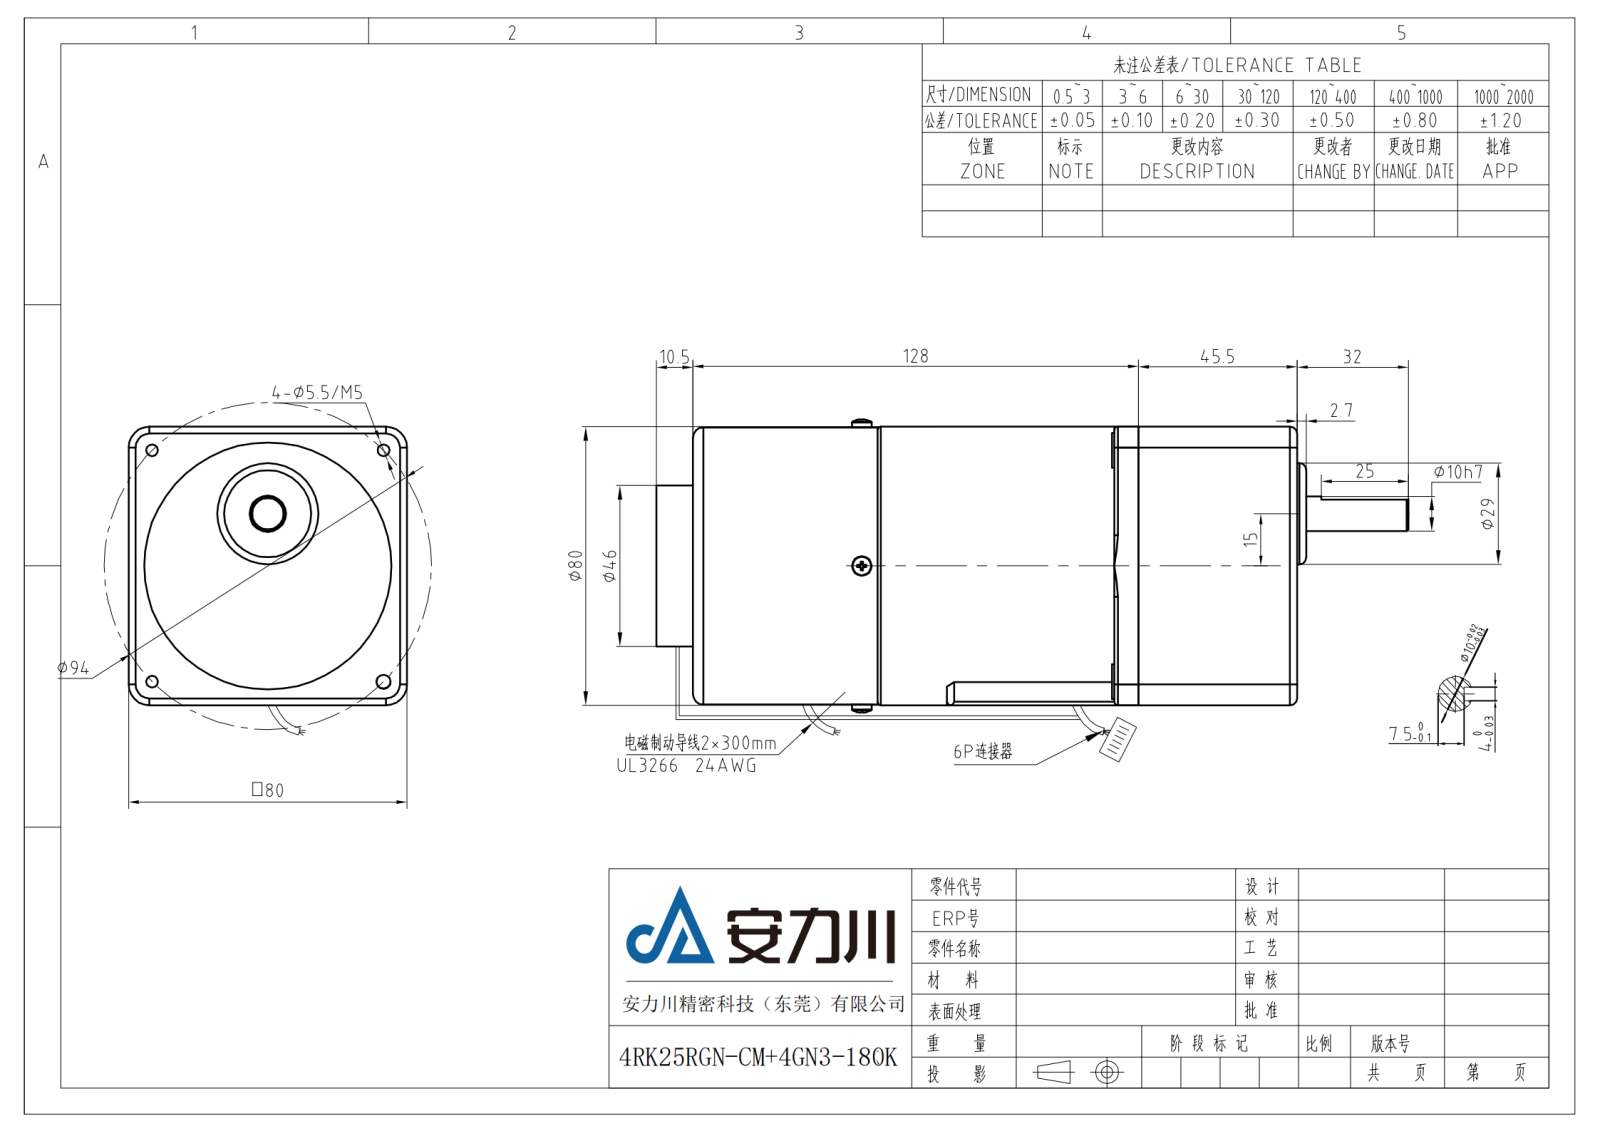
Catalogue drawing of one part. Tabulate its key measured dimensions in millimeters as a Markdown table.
| quantity | value |
| --- | --- |
| part name | 4RK25RGN-CM+箱体 |
| STEP written by | SolidWorks 2020 (CONFIG_CONTROL_DESIGN) |
| units | millimeters |
| bodies | 0 solids, 295 faces (114 planar, 111 cylindrical, 70 other) |
| overall size | 215.9 × 84.31 × 84.31 |
| round holes (diameter × count) | 3.3 × 4, 3.39 × 3, 10.5 × 2, 4.06 × 1, 4.2 × 1, 5.5 × 1, 7 × 1, 12 × 1, 22 × 1, 23.3 × 1, 26 × 1, 30 × 1 |
| round bosses / shafts (diameter × count) | 10 × 5, 9.76 × 4, 8.5 × 4, 5.6 × 2, 80 × 1, 79.6 × 1, 58.2 × 1, 46.2 × 1 |
| partial cylindrical surfaces (radius × count) | 1 × 7, 2 × 4, 6 × 4, 8.25 × 1 |
| main face-to-face distances | 80, 0.8, 171.6, 44.7, 69.7, 101.1, 170.8, 101.9, 121.9, 121.1 |
| hole center spacings | 16.77, 30, 33, 36.9, 44.6, 46.99, 47, 58.57 |
